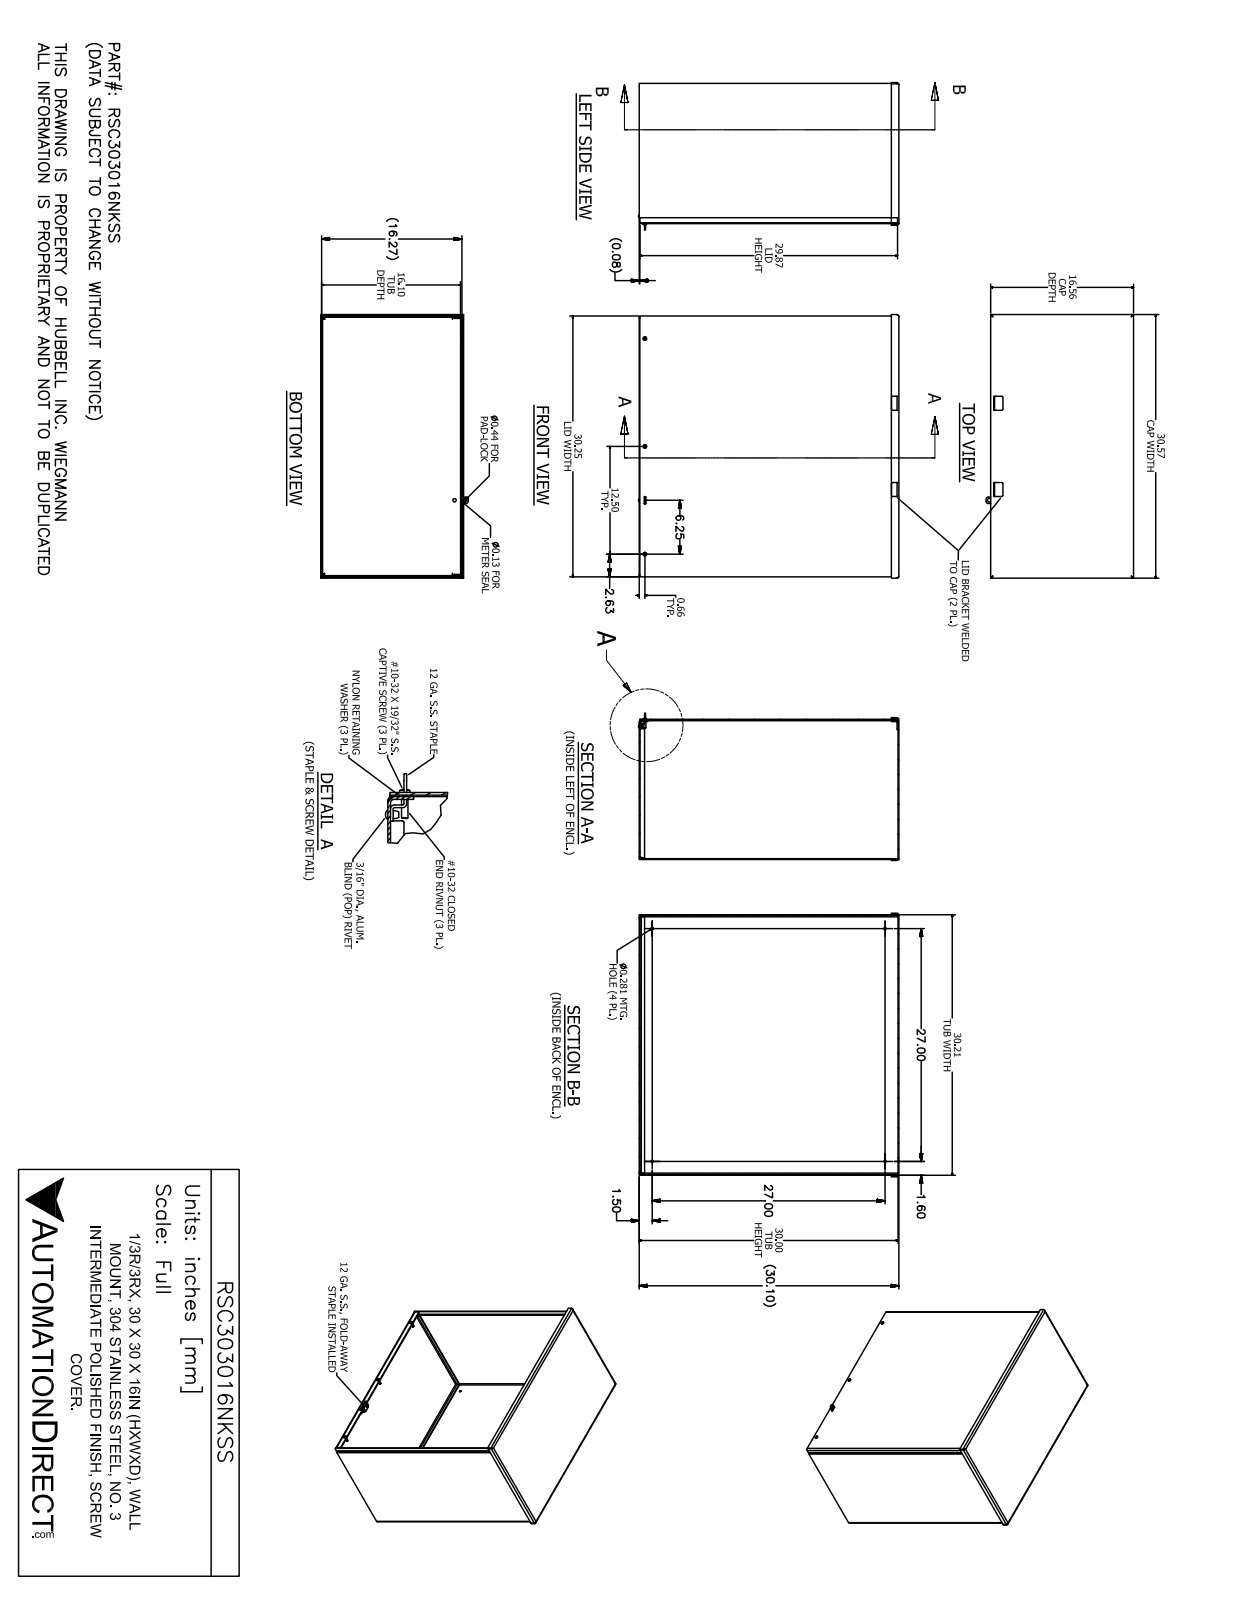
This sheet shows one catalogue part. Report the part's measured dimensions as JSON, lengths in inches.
{"part_name": "RSC303016NKSS", "step_written_by": "SolidWorks 2017 (AUTOMOTIVE_DESIGN)", "units": "inches", "bodies": {"solids": 17, "faces": 440, "planar": 241, "cylindrical": 117, "other": 82}, "overall_size": [30.572, 30.194, 17.094], "volume_in3": 406, "surface_area_in2": 7869, "round_holes": [[0.25, 6], [0.281, 4], [0.156, 3], [0.196, 3], [0.257, 3], [0.278, 3], [0.125, 1], [0.198, 1], [0.201, 1], [0.437, 1]], "round_bosses_or_shafts": [[0.453, 3], [0.406, 3], [0.248, 3], [0.167, 3], [0.187, 1]], "partial_cylinders_radius": [[0.141, 14], [0.245, 14], [0.125, 9], [0.031, 6], [0.25, 4], [0.089, 3], [0.047, 2], [0.062, 2]], "face_to_face_distances": [0.104, 16.162, 30, 30.104, 16.266, 16.058, 29.896, 30.208, 0.111, 29.993], "hole_center_spacings": [12.5, 27, 31.321, 28.719, 1.308, 1.329, 13.526, 13.528]}
